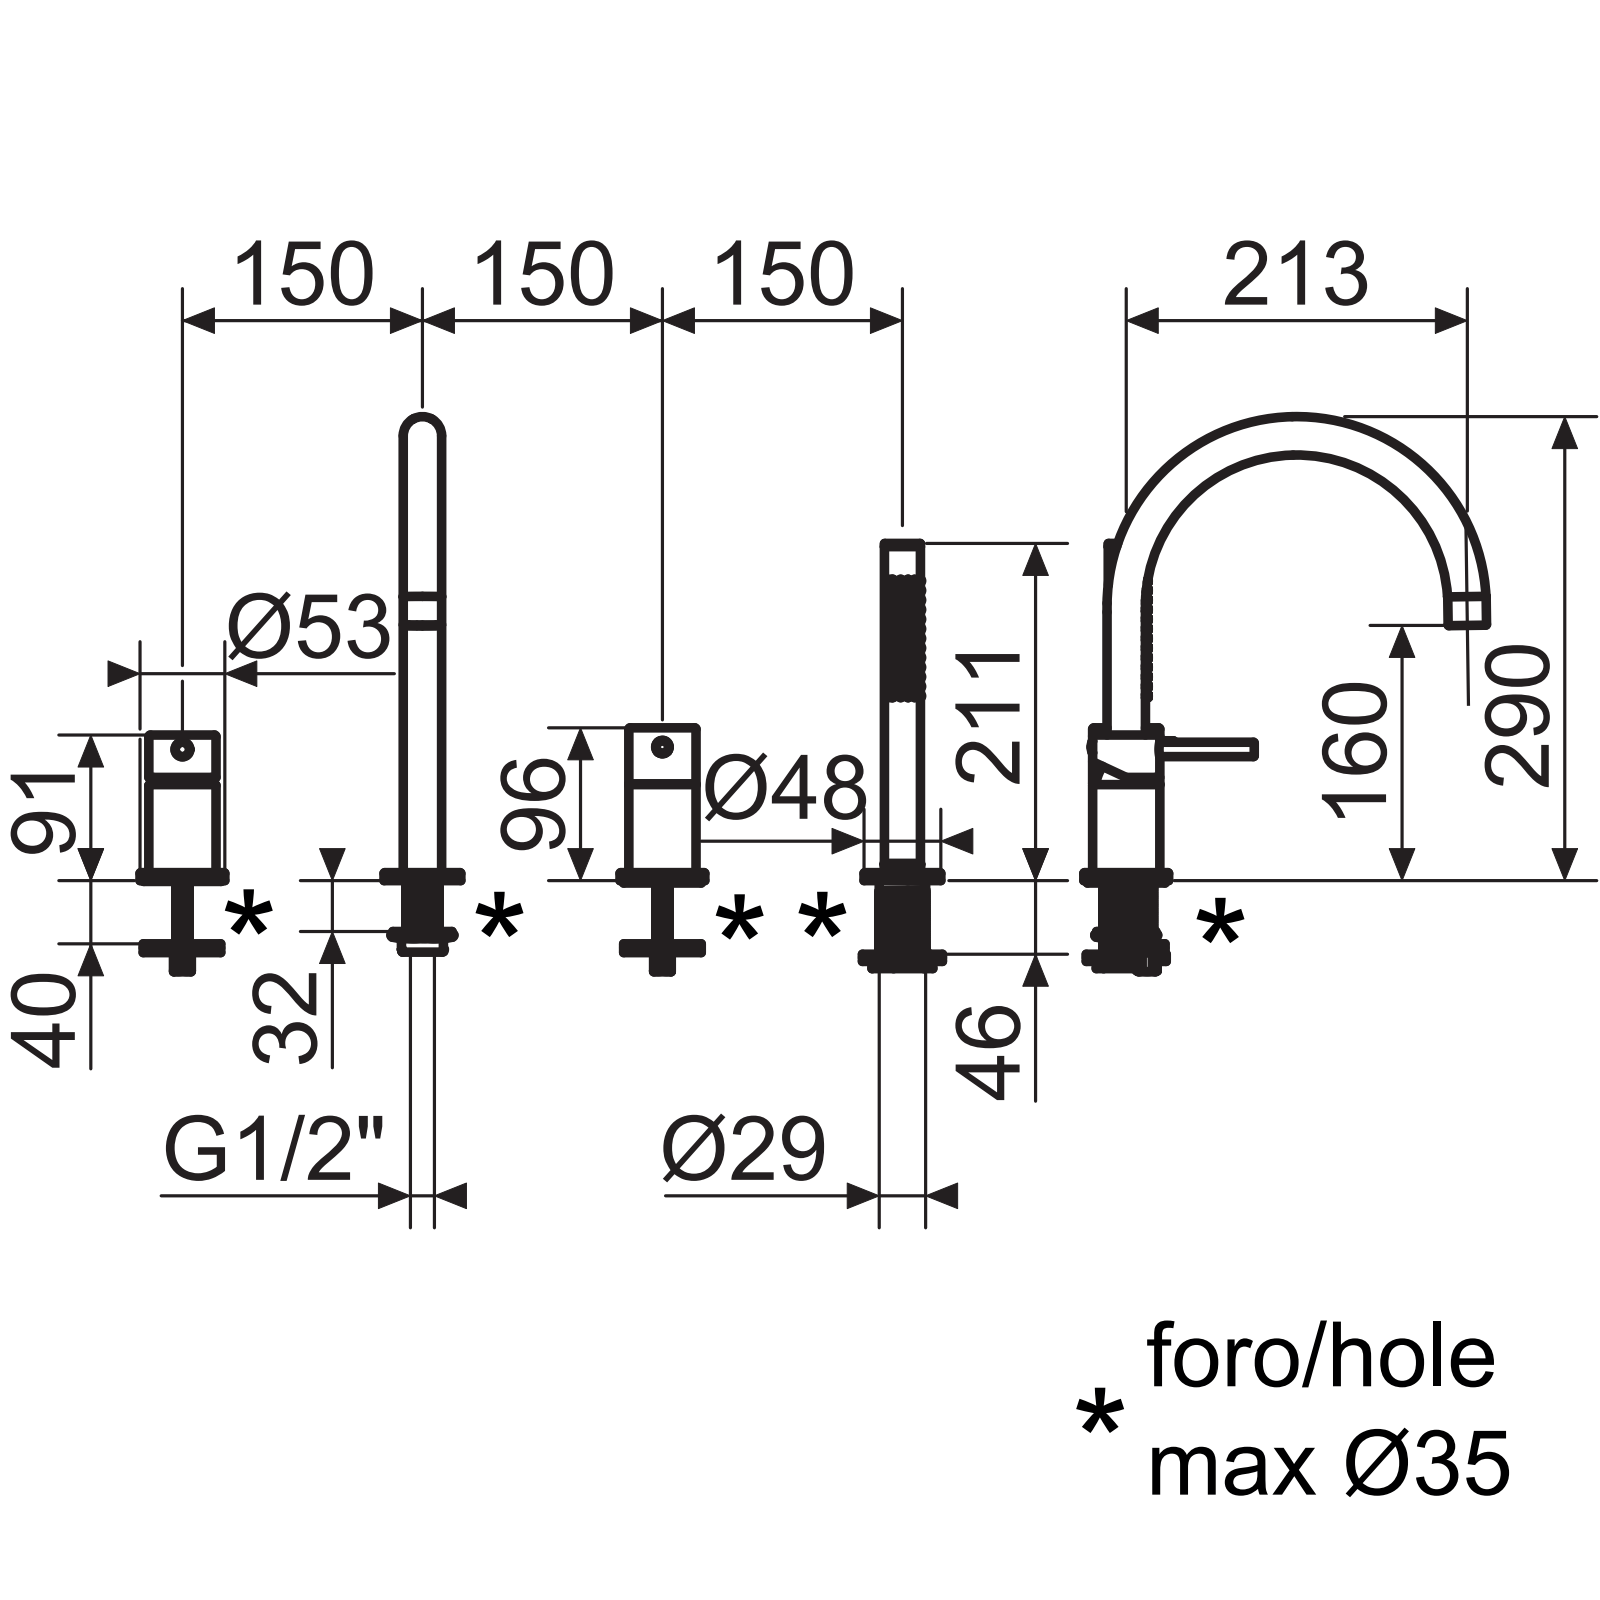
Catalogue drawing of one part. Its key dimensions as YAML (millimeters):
part_name: "TOM111C0A4FSDX1_1; TOM111C0A4FSDX1_6; TOM111C0A4FSDX1_7; DQ211 (+8 more)"
step_written_by: "CREO PARAMETRIC BY PTC INC, 2020281 (CONFIG_CONTROL_DESIGN)"
units: millimeters
bodies: {solids: 22, faces: 1969, planar: 1130, cylindrical: 641, other: 198}
overall_size: [500.5, 307.65, 251.68]
volume: 329416
surface_area: 176691
round_holes:
  - {diameter: 0.6, count: 65}
  - {diameter: 36, count: 3}
  - {diameter: 17, count: 2}
  - {diameter: 38.5, count: 2}
  - {diameter: 45, count: 2}
  - {diameter: 4.1, count: 1}
  - {diameter: 4.2, count: 1}
  - {diameter: 4.4, count: 1}
  - {diameter: 5, count: 1}
  - {diameter: 5.2, count: 1}
  - {diameter: 6, count: 1}
  - {diameter: 8.2, count: 1}
round_bosses_or_shafts:
  - {diameter: 2, count: 65}
  - {diameter: 53, count: 2}
  - {diameter: 48, count: 2}
  - {diameter: 42, count: 2}
  - {diameter: 39, count: 2}
  - {diameter: 24, count: 2}
  - {diameter: 3, count: 2}
  - {diameter: 41.6, count: 1}
partial_cylinders:
  - {radius: 1, count: 13}
  - {radius: 5, count: 1}
  - {radius: 6.5, count: 1}
  - {radius: 8.25, count: 1}
  - {radius: 9, count: 1}
  - {radius: 13.75, count: 1}
face_to_face_distances: [2.5, 0.5, 54.5, 2, 1.5, 1, 90.5, 93, 5, 59.5]
hole_center_spacings: [7.5, 12.82, 18.55, 6, 12, 24.42, 30.34, 18]
